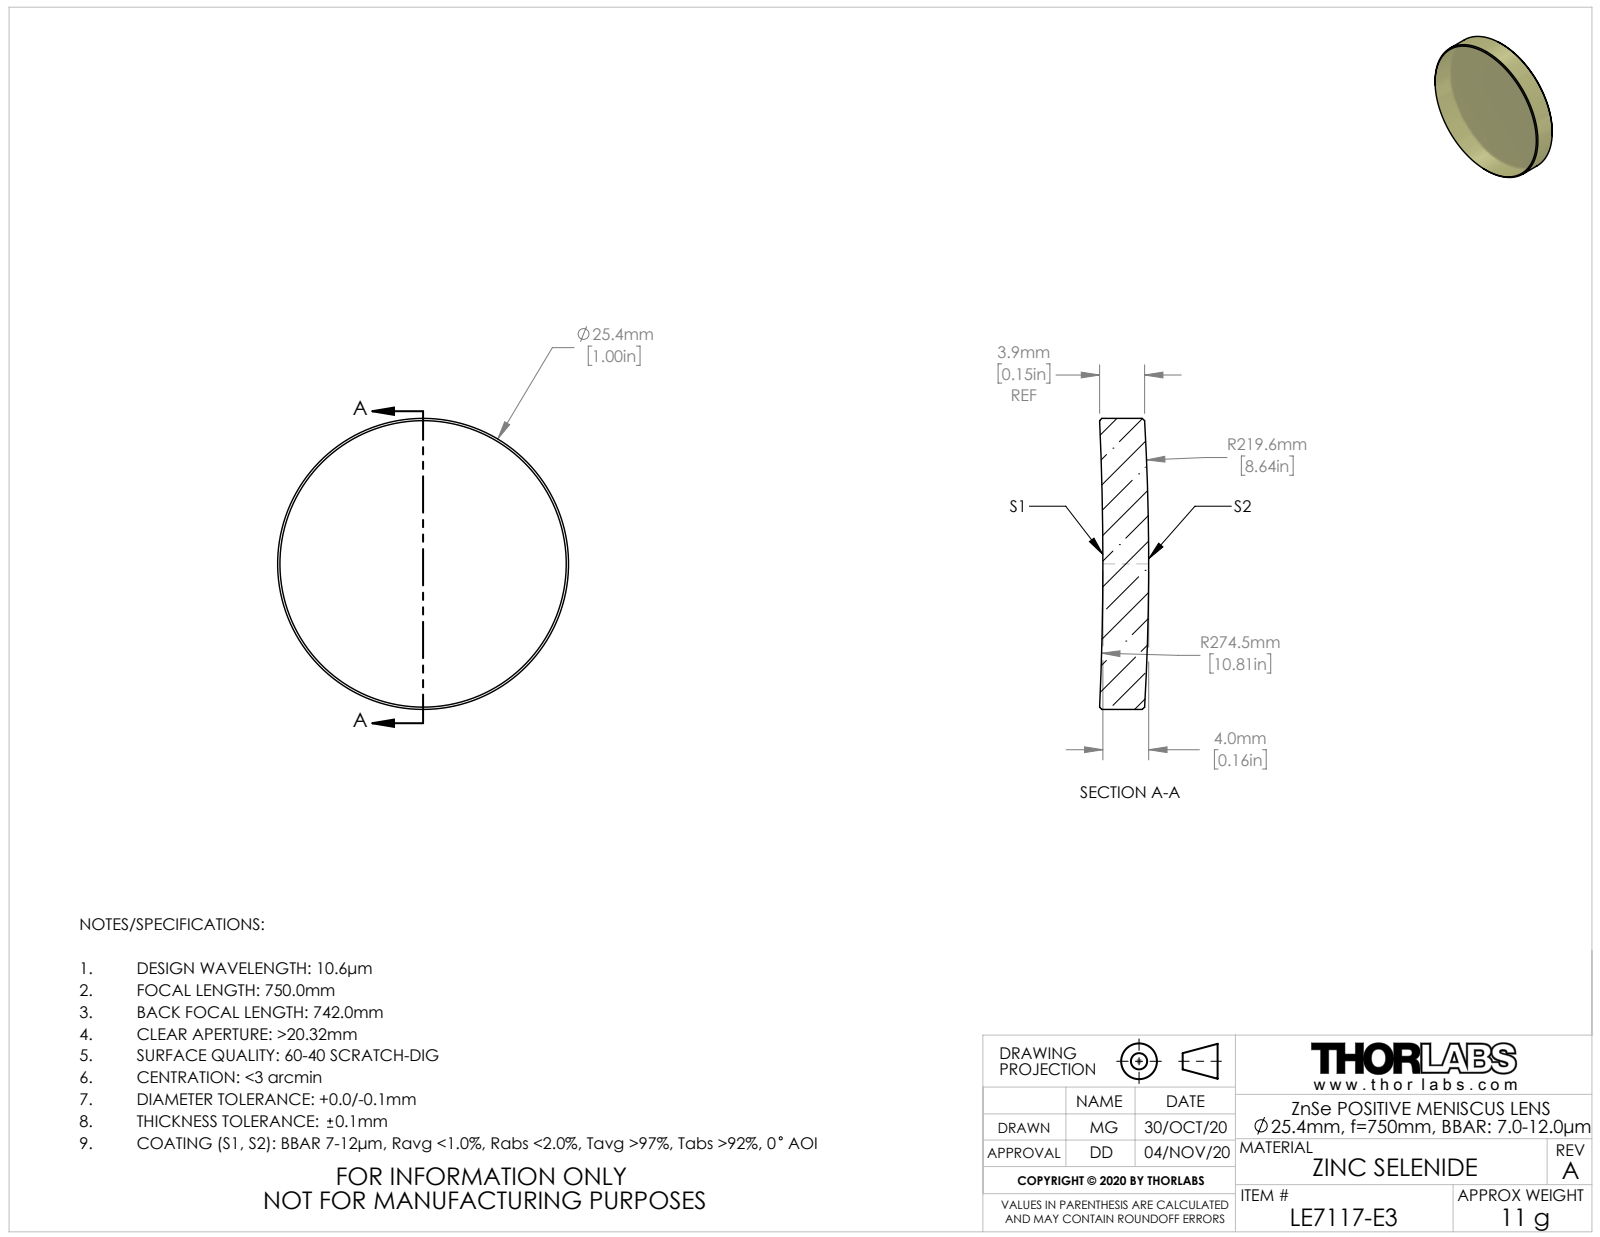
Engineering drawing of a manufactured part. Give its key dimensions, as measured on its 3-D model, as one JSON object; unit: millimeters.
{"part_name": "TTN225634-E0W", "step_written_by": "SolidWorks 2018 (CONFIG_CONTROL_DESIGN)", "units": "millimeters", "bodies": {"solids": 1, "faces": 10, "planar": 0, "cylindrical": 2, "other": 8}, "overall_size": [25.4, 25.4, 4.29], "volume_mm3": 2005, "surface_area_mm2": 1309, "round_bosses_or_shafts": [[25.4, 1]]}
